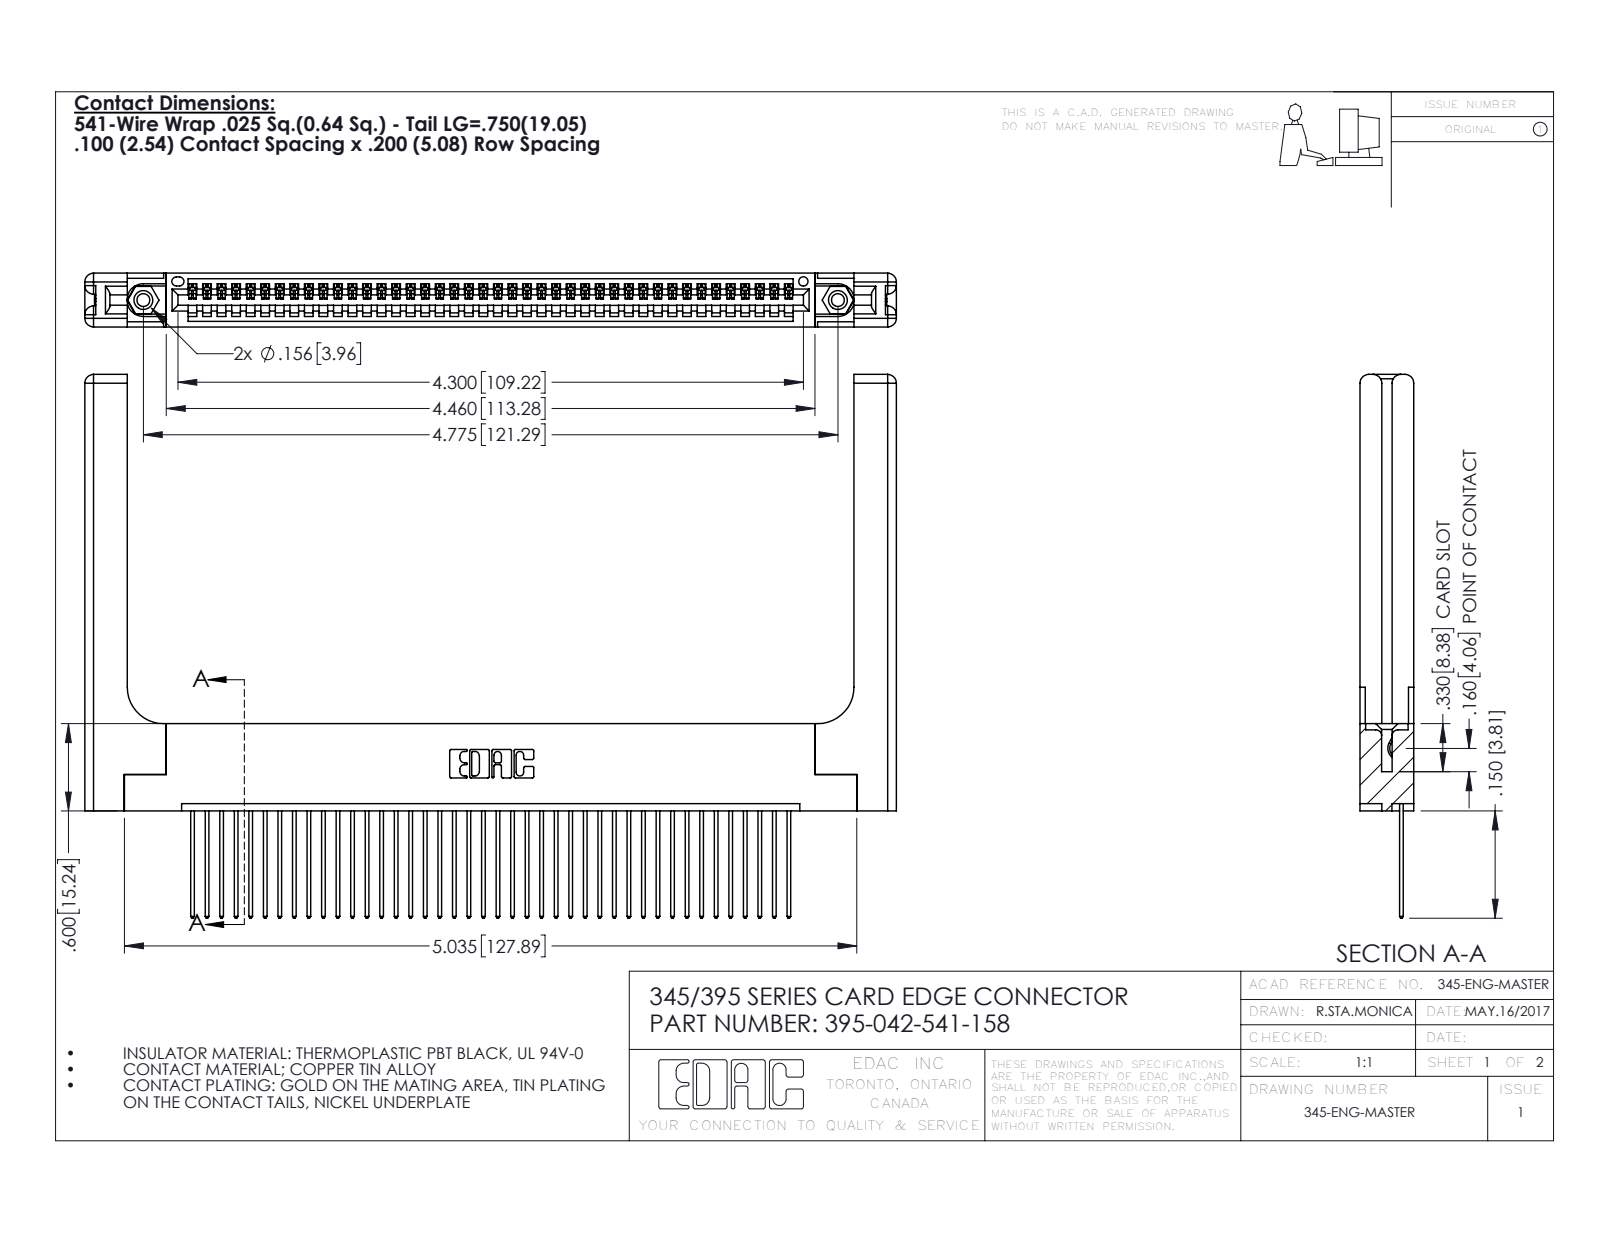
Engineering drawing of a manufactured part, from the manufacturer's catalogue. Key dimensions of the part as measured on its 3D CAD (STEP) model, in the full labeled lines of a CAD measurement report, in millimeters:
Part name (STEP PRODUCT): 345-220-058_345-220-058; 395-042-541-158; 345 Part_Flush Mounting Lugs - 0.156 Dia-TH; 345-292-001_345-293-141 (+1 more)
STEP written by: SolidWorks 2016 (CONFIG_CONTROL_DESIGN)
Units: millimetres
Bodies: 47 solids, 2818 faces (1908 planar, 850 cylindrical, 60 other)
Overall size (bounding box): 141.7 × 94.9 × 9.4
Volume: 22 110 mm³ · Surface area: 24 190 mm²
Round holes (diameter × count): ⌀2.3 ×2, ⌀3.2 ×2, ⌀4 ×2, ⌀1.6 ×1
Round bosses / shafts (diameter × count): ⌀3.9 ×2
Partial cylindrical surfaces — rounded edges, fillets, slot ends (radius × count): R0.2 ×84, R0.3 ×84, R0.3 ×22, R1.5 ×16, R0.2 ×6, R0.8 ×6, R0.7 ×3, R0.8 ×2
Main face-to-face distances: 1.8, 9.4, 7.6, 2.5, 6.9, 0.6, 5.1, 3.8, 3.8, 5.7
Hole centre spacings: 6.9, 115.3, 121.3
